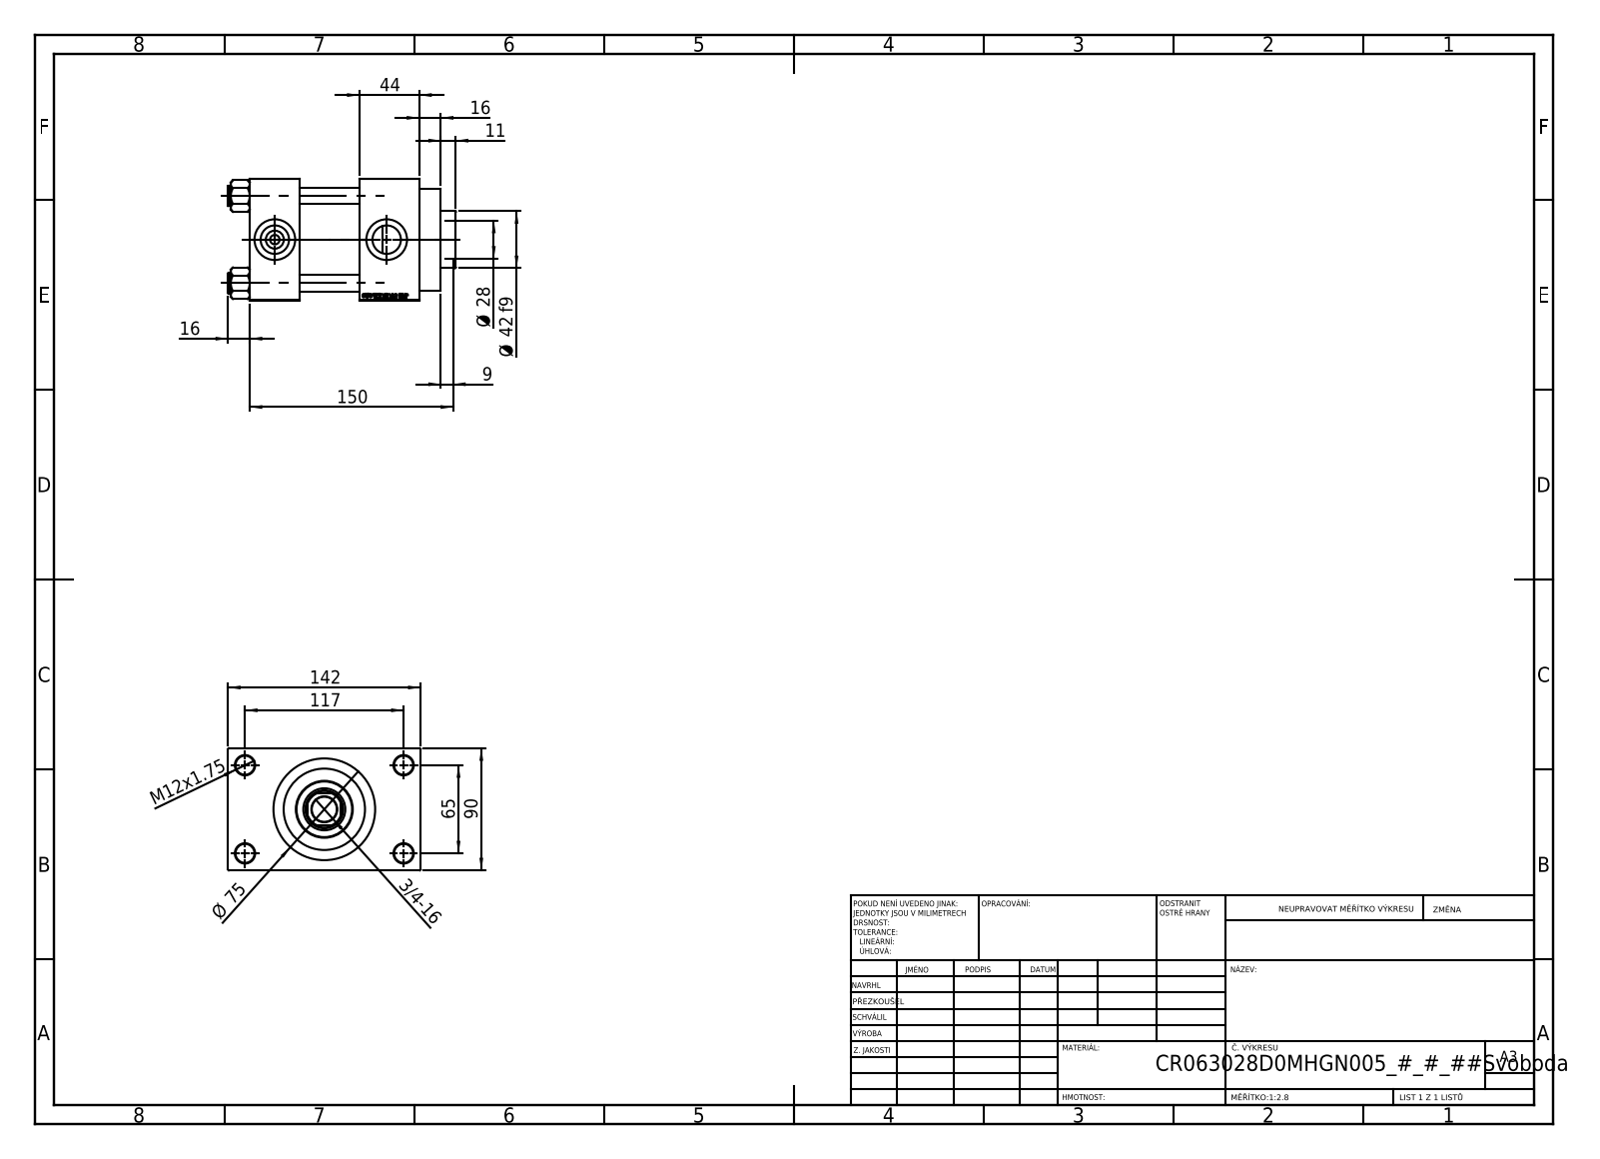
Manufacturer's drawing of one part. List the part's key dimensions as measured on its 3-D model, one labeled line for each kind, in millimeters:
Part name (STEP PRODUCT): V215CR_D_TYCINKA; V215_VC_A; V215CR_VCP_D; V215CR_D_Body (+1 more)
STEP written by: SolidWorks 2019 (CONFIG_CONTROL_DESIGN)
Units: millimetres
Bodies: 11 solids, 1103 faces (497 planar, 88 cylindrical, 518 other)
Overall size (bounding box): 168 × 142 × 90
Volume: 1 027 000 mm³ · Surface area: 187 257 mm²
Round holes (diameter × count): ⌀12 ×4, ⌀14 ×4, ⌀7 ×2, ⌀20.96 ×2, ⌀30 ×2, ⌀18.5 ×1, ⌀28 ×1, ⌀31 ×1, ⌀50 ×1, ⌀60 ×1, ⌀63 ×1
Round bosses / shafts (diameter × count): ⌀15 ×4, ⌀75 ×1, ⌀69 ×1, ⌀42 ×1
Partial cylindrical surfaces — rounded edges, fillets, slot ends (radius × count): R13.5 ×1
Main face-to-face distances: 44, 90, 81, 37, 88, 125, 26, 116, 16, 141
Hole centre spacings: 26.35, 45.47, 64.3, 66.92, 69.81, 90.65, 111.34, 65
